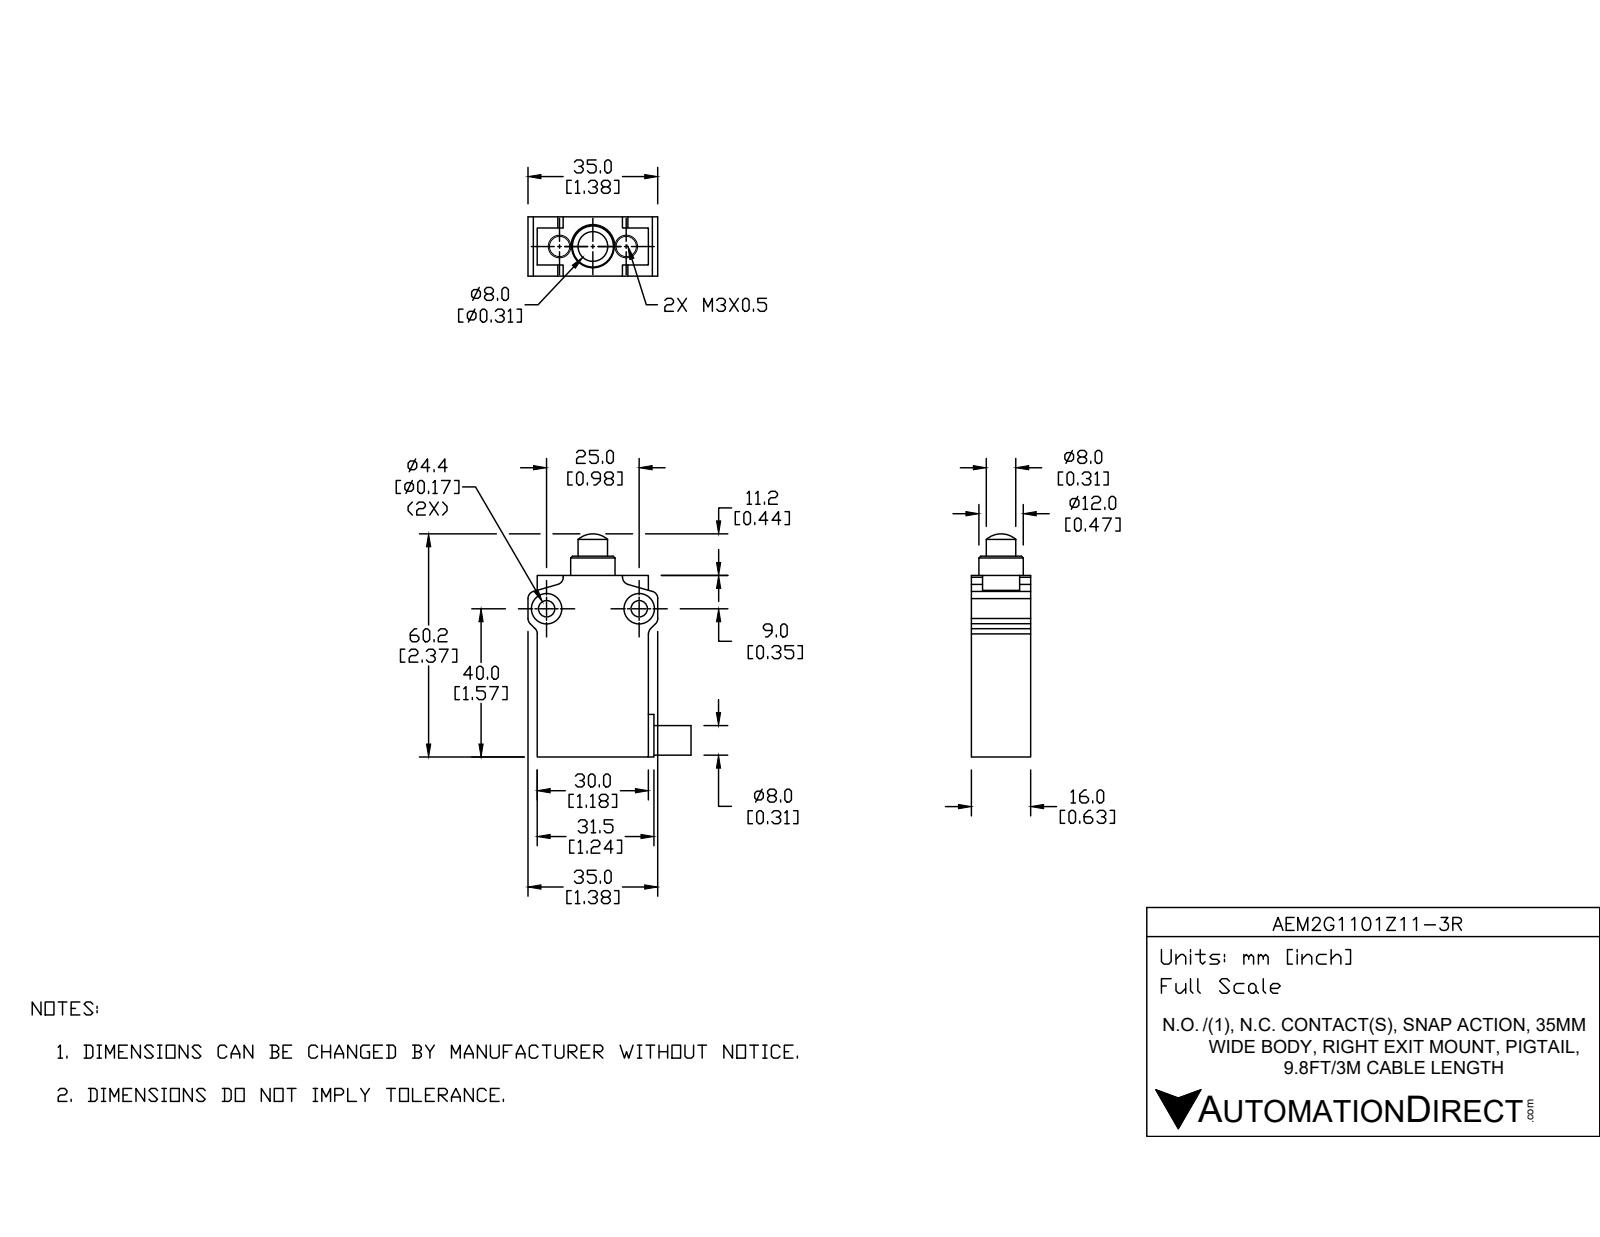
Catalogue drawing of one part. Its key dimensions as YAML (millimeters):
part_name: "AEM2G1101Z11-3R"
step_written_by: "SolidWorks 2017 (AUTOMOTIVE_DESIGN)"
units: millimeters
bodies: {solids: 4, faces: 79, planar: 38, cylindrical: 39, other: 2}
overall_size: [60, 47.5, 16]
volume: 23630
surface_area: 7600
round_holes:
  - {diameter: 3, count: 2}
  - {diameter: 4.4, count: 2}
  - {diameter: 8.2, count: 2}
  - {diameter: 8, count: 1}
round_bosses_or_shafts:
  - {diameter: 12, count: 1}
  - {diameter: 8.2, count: 1}
partial_cylinders:
  - {radius: 2, count: 8}
  - {radius: 6.5, count: 1}
face_to_face_distances: [16, 30, 49, 12, 2.5, 32.5, 4, 44.2, 4.8, 54]
hole_center_spacings: [9.5, 19, 25]
